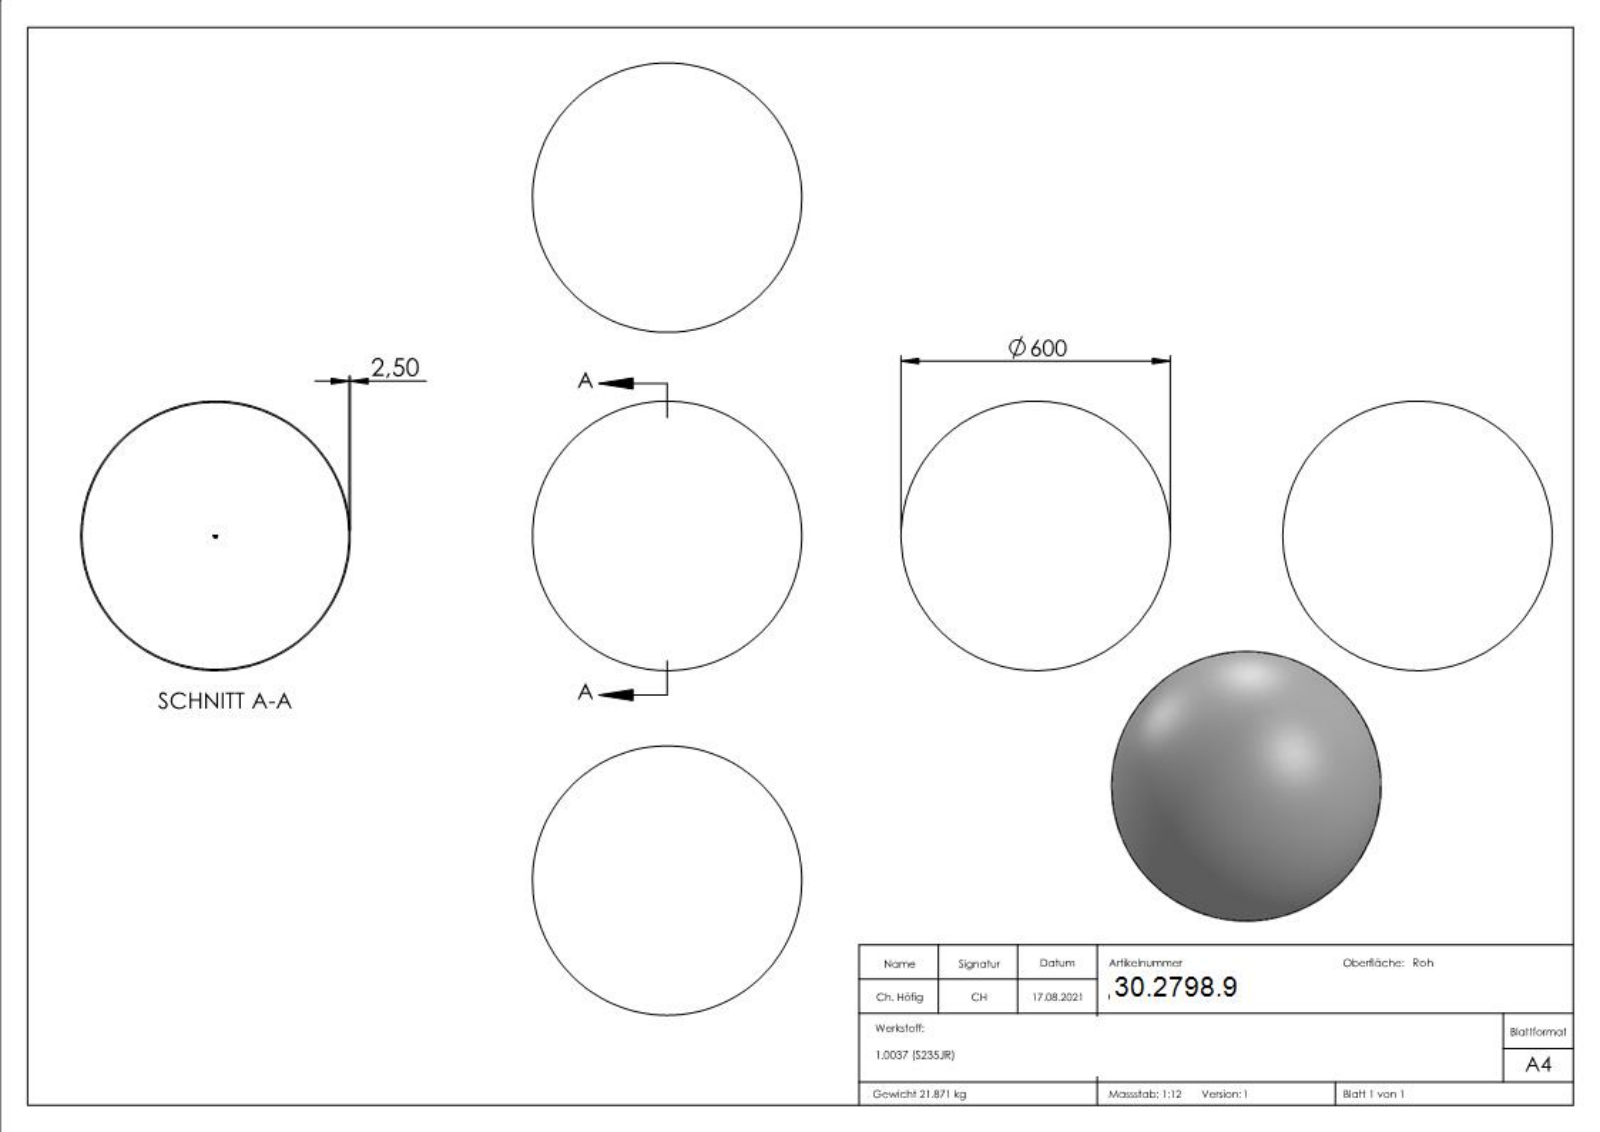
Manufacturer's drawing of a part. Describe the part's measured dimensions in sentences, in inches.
The part is named "600-EHK". Its 3-D file was written by "SolidWorks 2018 (CONFIG_CONTROL_DESIGN)". It is 1 solid with 194 faces: 96 planar, 0 cylindrical and 98 other. Overall it measures 23.622 by 23.622 by 23.622 inches. Its volume is 171.1 cubic inches and its surface area 3 477 square inches. The main face-to-face distances are 0.126, 0.05, 0.177, 0.018, 0.141, 0.123, 0.027, 0.025, 0.137, 0.053.
